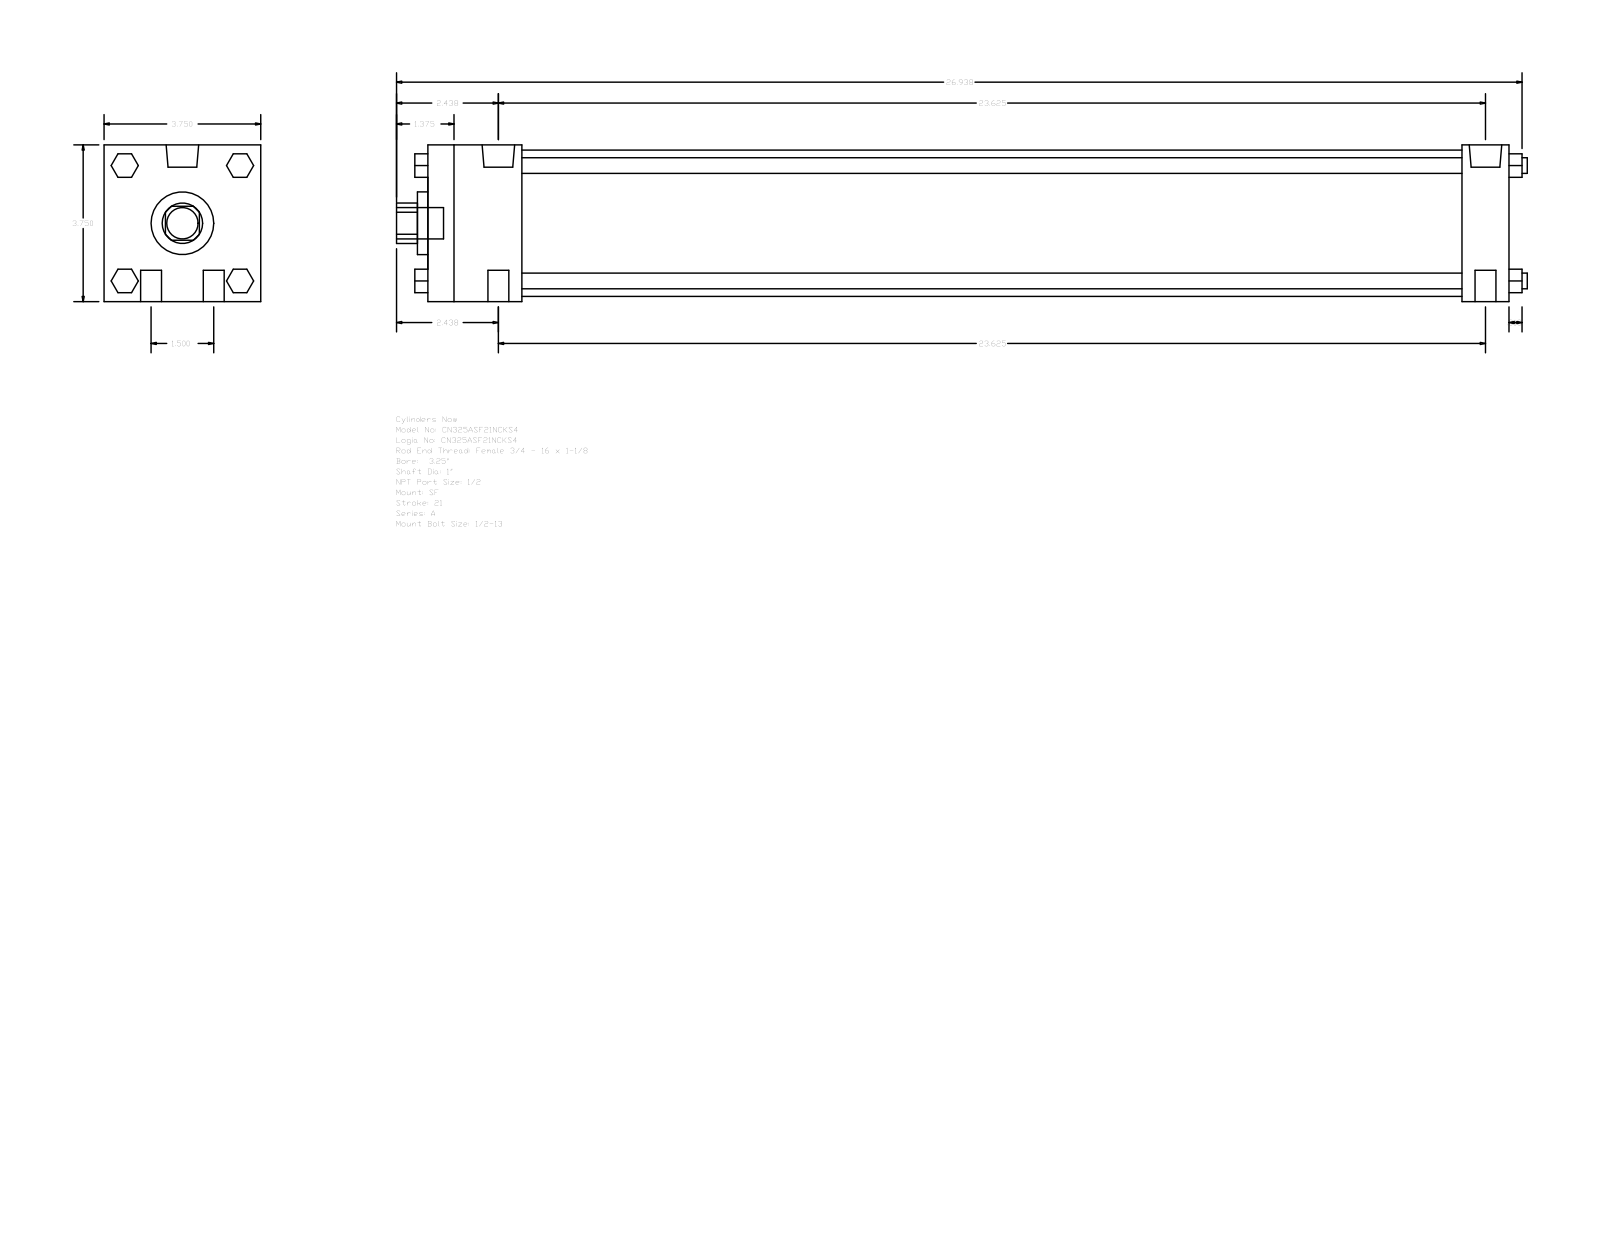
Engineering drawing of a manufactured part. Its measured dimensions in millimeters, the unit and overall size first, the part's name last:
Units: millimetres
Overall size (bounding box): 687.39 × 95.25 × 95.25
Round holes (diameter × count): ⌀25.4 ×1, ⌀38.1 ×1, ⌀88.9 ×1
Round bosses / shafts (diameter × count): ⌀12.7 ×4, ⌀9.53 ×4, ⌀19.77 ×2, ⌀8.73 ×2, ⌀19.05 ×1
Partial cylindrical surfaces — rounded edges, fillets, slot ends (radius × count): R12.29 ×1
Main face-to-face distances: 95.24, 657.22, 28.57, 628.65, 57.15, 571.5, 600.07, 14.28, 35.05, 60.71
Bodies: 0 solids, 124 faces (94 planar, 30 cylindrical, 0 other)
Part name (STEP PRODUCT): A_SF__0325_1
STEP written by: GSSL Pune (CONFIG_CONTROL_DESIGN)
